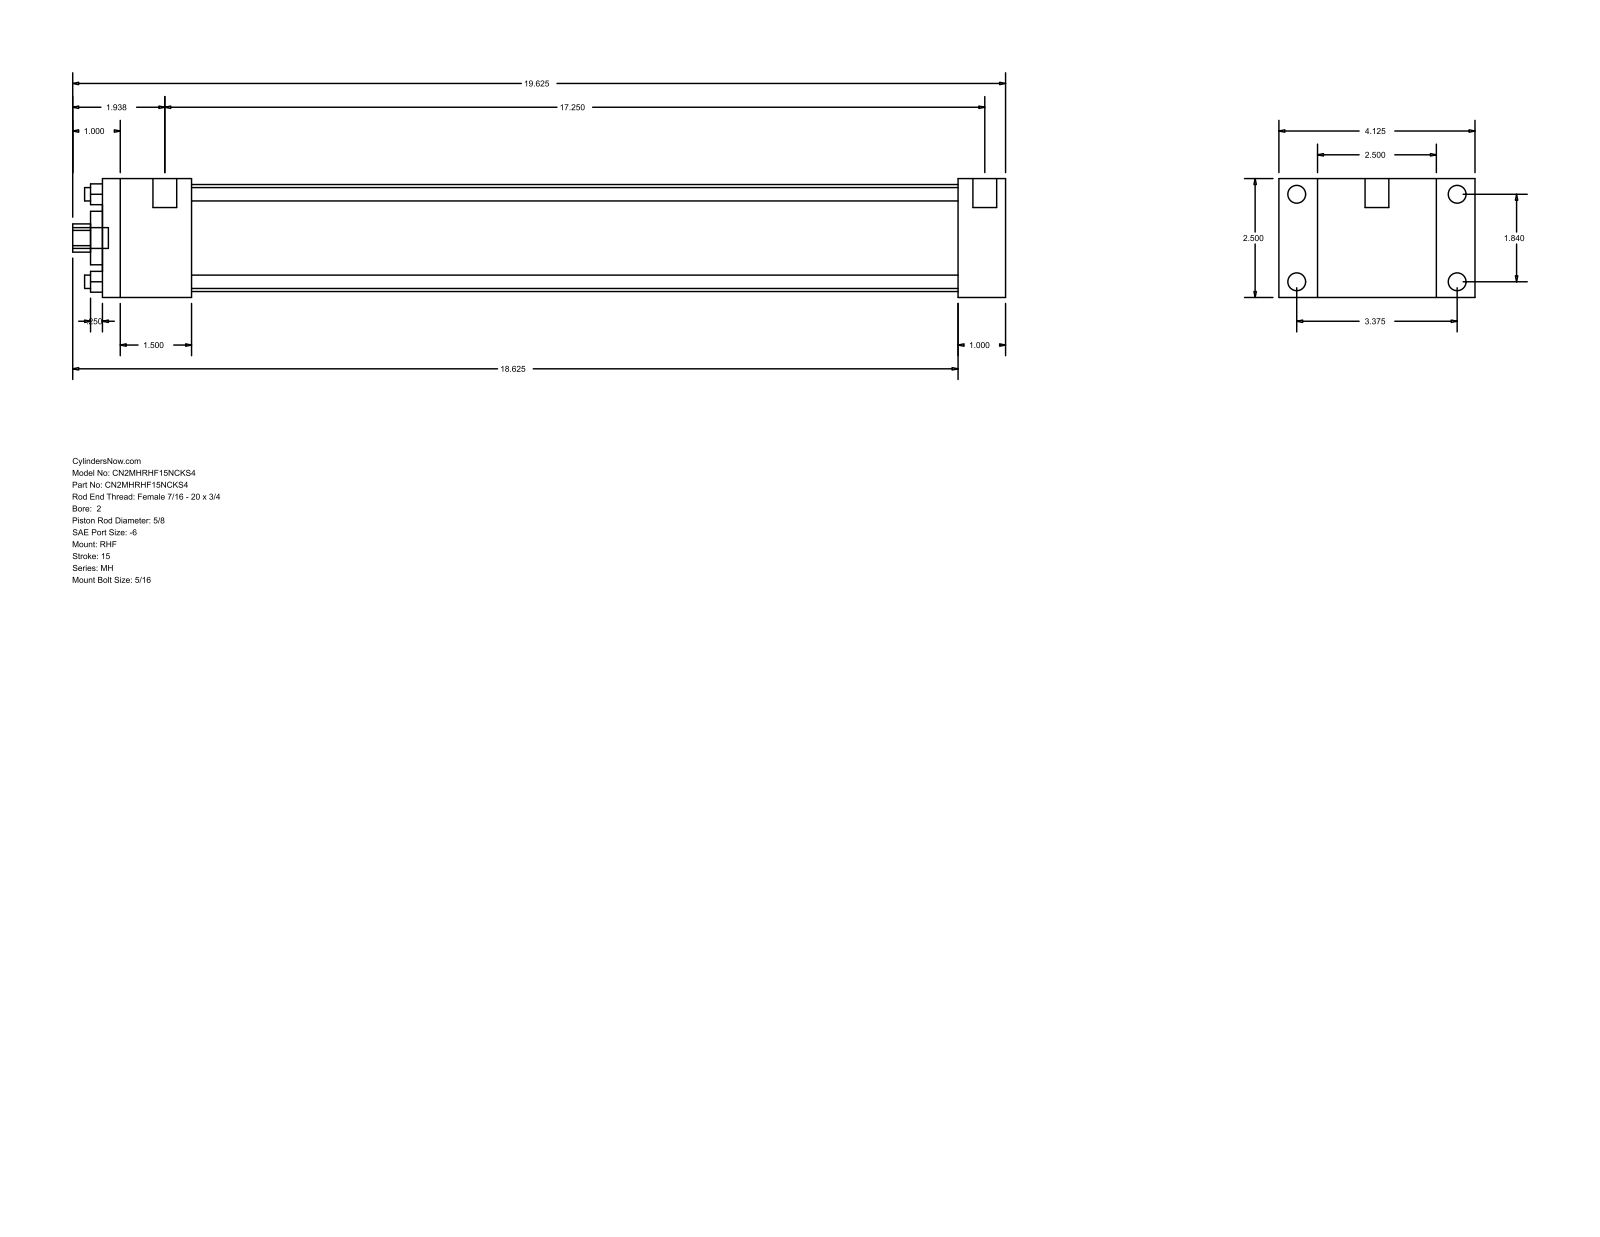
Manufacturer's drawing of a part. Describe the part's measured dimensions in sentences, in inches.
The part is named "MH_RHF__0200_0.625". Its 3-D file was written by "GSSL Pune (CONFIG_CONTROL_DESIGN)". It is 0 solids with 88 faces: 60 planar, 28 cylindrical and 0 other. Overall it measures 19.625 by 4.125 by 2.5 inches. Round holes: 4 of diameter 0.281, 1 of diameter 0.625, 1 of diameter 1.125, 1 of diameter 2.25. Round bosses or shafts: 4 of diameter 0.375, 4 of diameter 0.219, 2 of diameter 0.5, 1 of diameter 0.437. Partial cylindrical surfaces (rounded edges, fillets, slot ends): 1 of radius 0.297. The main face-to-face distances are 2.5, 1, 0.813, 3.313, 18, 19, 4.125, 1.875, 16.125, 17.125. The hole center spacings are 1.301, 1.84, 2.602.
